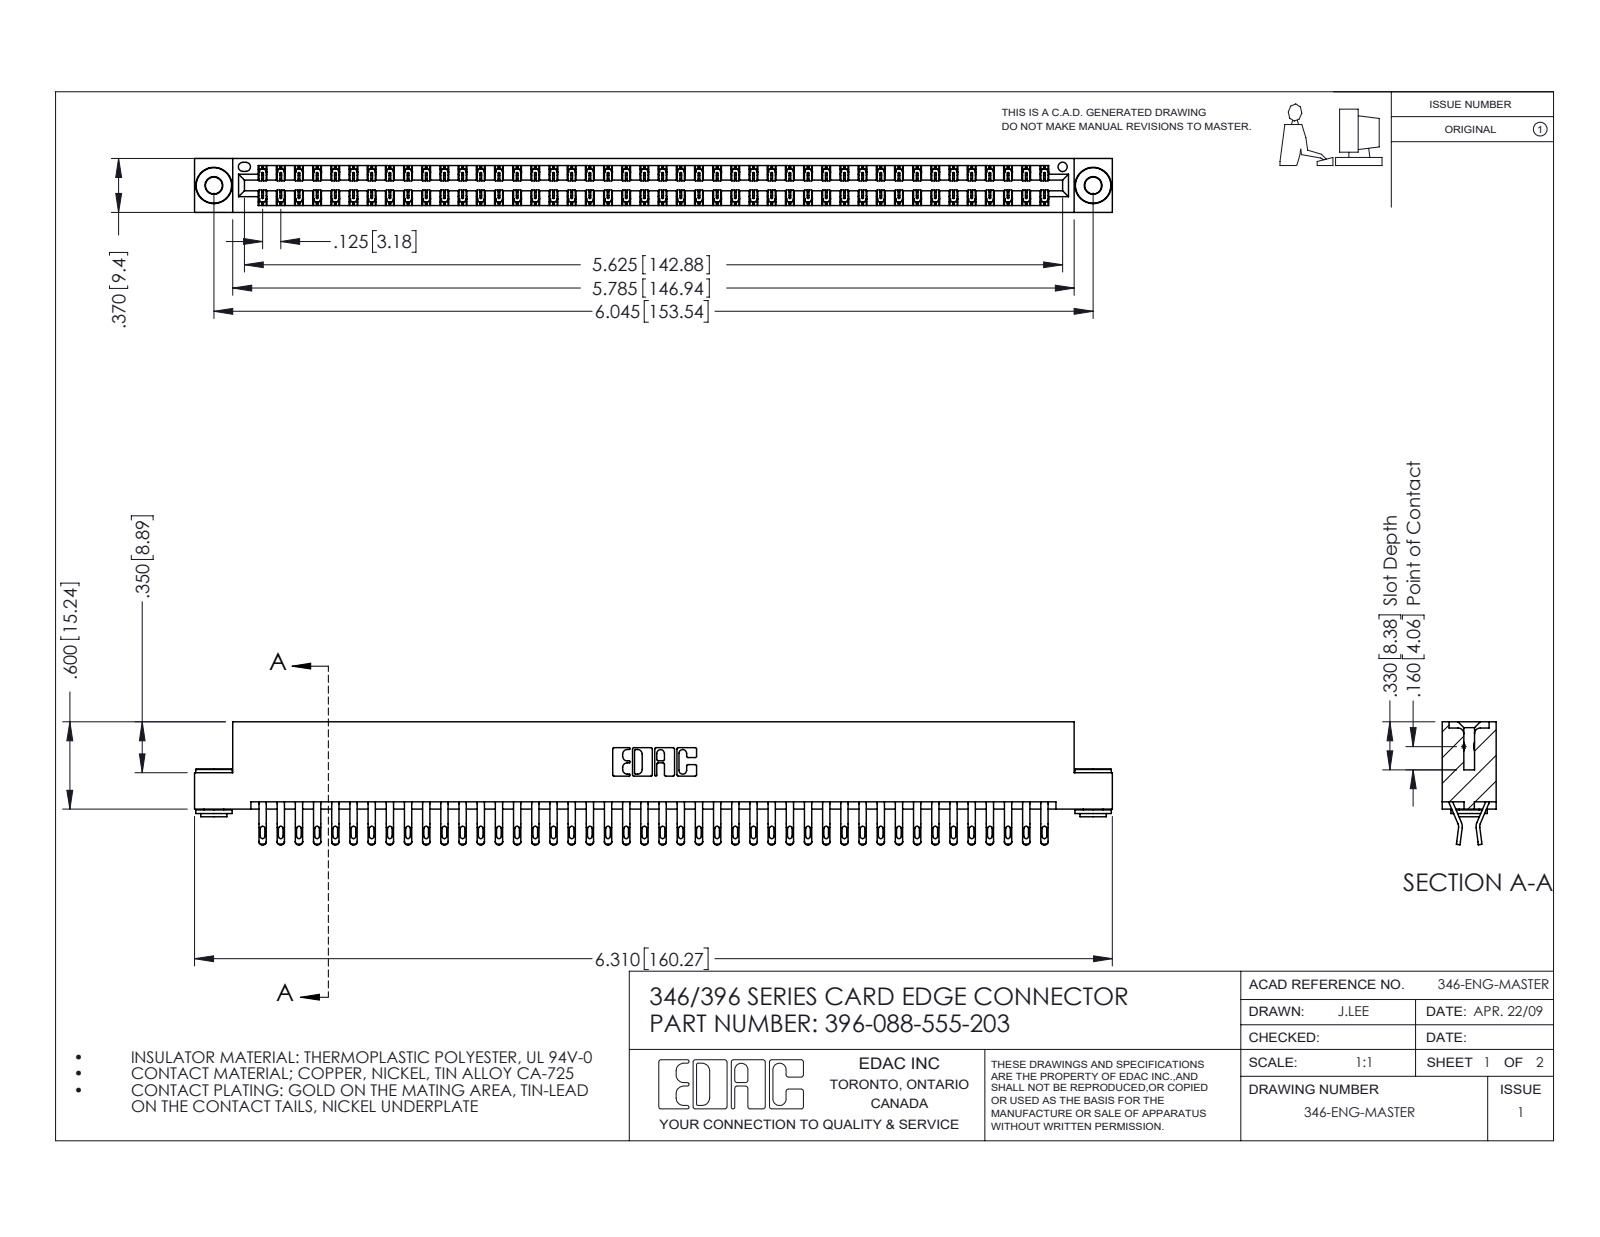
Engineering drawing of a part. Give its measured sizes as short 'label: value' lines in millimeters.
name: 396-088-555-203; 345-292-001_555 Tail; 345-250-002_345-250-002-102; 346 Part_Flush Mounting Lugs - 0.156 Dia-TH
written by: SolidWorks 2016 (CONFIG_CONTROL_DESIGN)
unit: mm
bodies: 91 solids, 5264 faces (2990 planar, 2266 cylindrical, 8 other)
size: 160.3 × 21.5 × 9.4
volume: 15 900 mm³; area: 23 040 mm²
holes: 2× ⌀2.9, 2× ⌀4, 1× ⌀1.6
bosses: 2× ⌀6.4, 2× ⌀4.6, 2× ⌀3.5
rounds: 176× R0.4, 176× R0.5, 132× R0.2, 22× R0.3, 6× R0.2, 6× R0.8, 3× R0.7, 2× R0.3
face distances: 1.2, 8.2, 9.4, 6.4, 0.6, 1.8, 7.6, 7, 3.8, 5.6
hole spacings: 6.2, 148.2, 153.5
